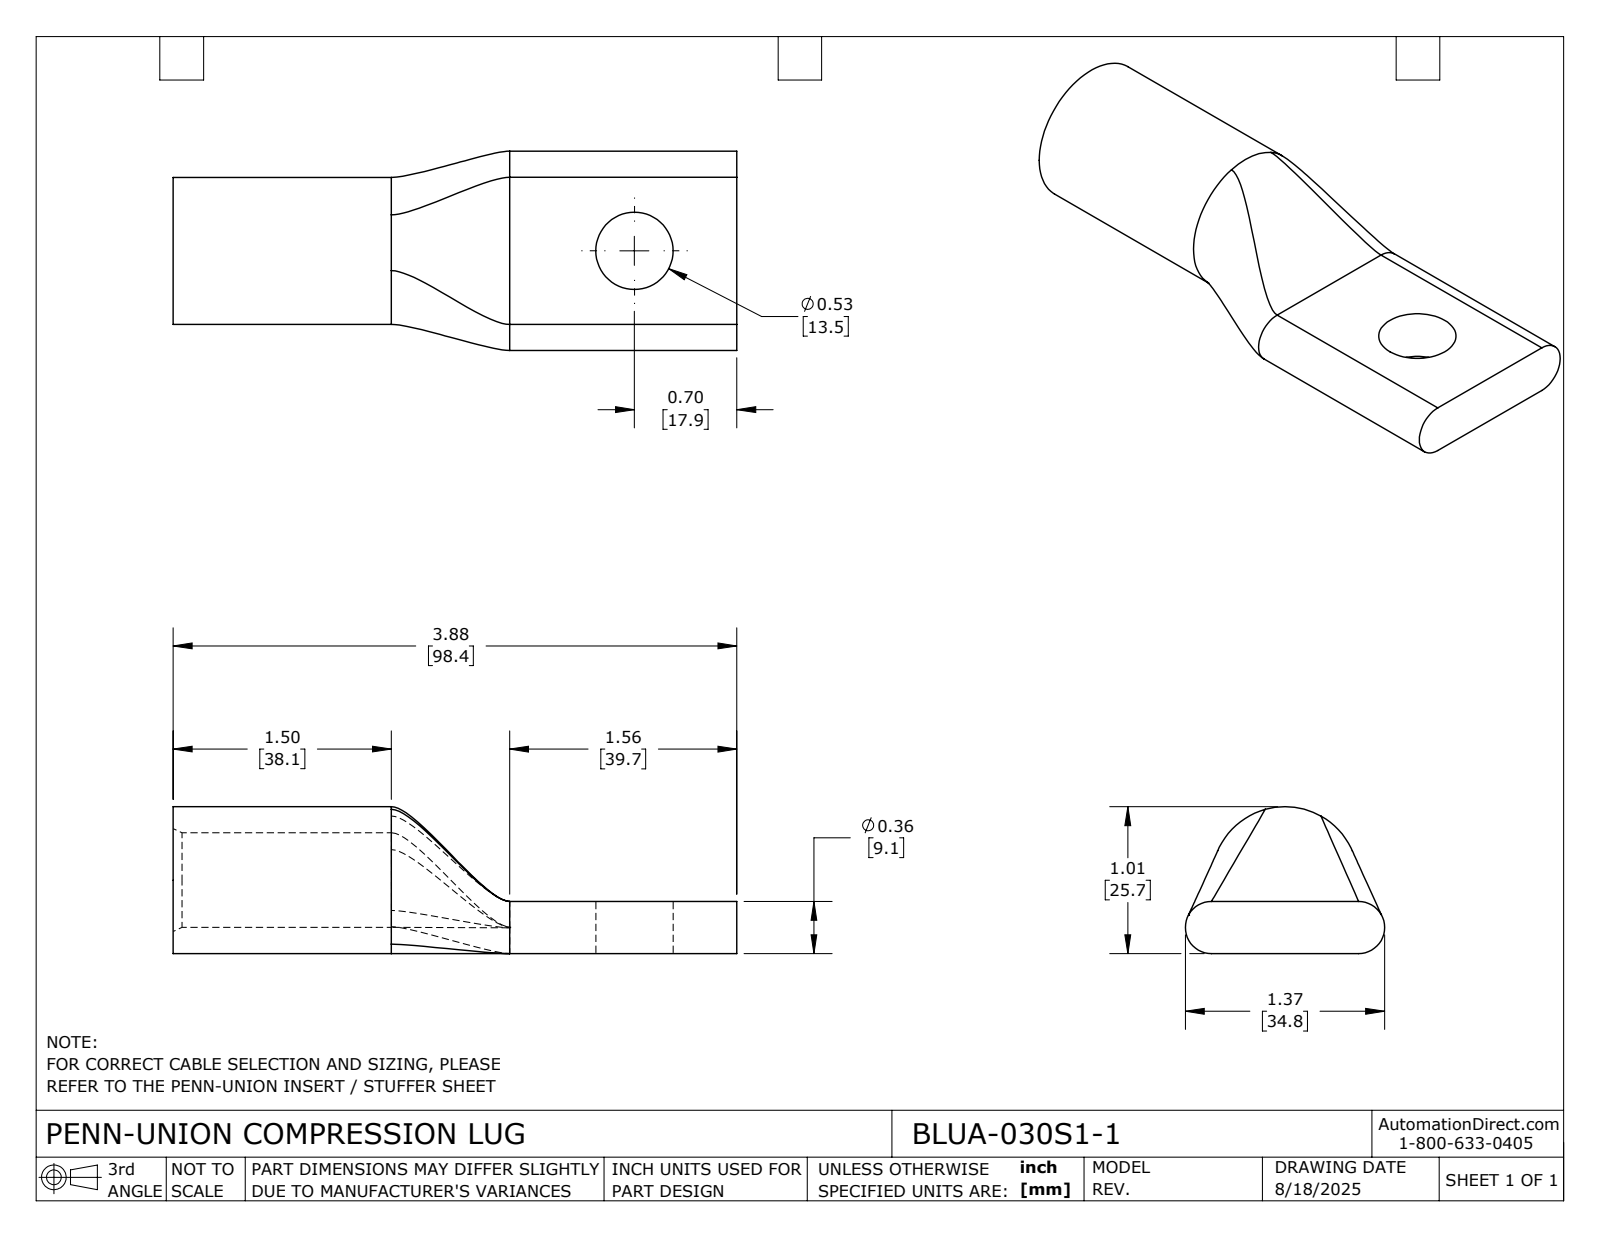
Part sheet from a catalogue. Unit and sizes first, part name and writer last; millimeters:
Units: millimetres
Overall size (bounding box): 98.4 × 34.8 × 25.7
Round holes (diameter × count): ⌀13.5 ×1, ⌀16.5 ×1
Round bosses / shafts (diameter × count): ⌀25.7 ×1
Partial cylindrical surfaces — rounded edges, fillets, slot ends (radius × count): R4.5 ×2
Main face-to-face distances: 9.1, 98.4, 58.8, 39.7
Volume: 28 250 mm³ · Surface area: 11 850 mm²
Bodies: 1 solid, 24 faces (5 planar, 9 cylindrical, 10 other)
Part name (STEP PRODUCT): BLUA-030S1-1
STEP written by: SolidWorks 2024 (CONFIG_CONTROL_DESIGN)
